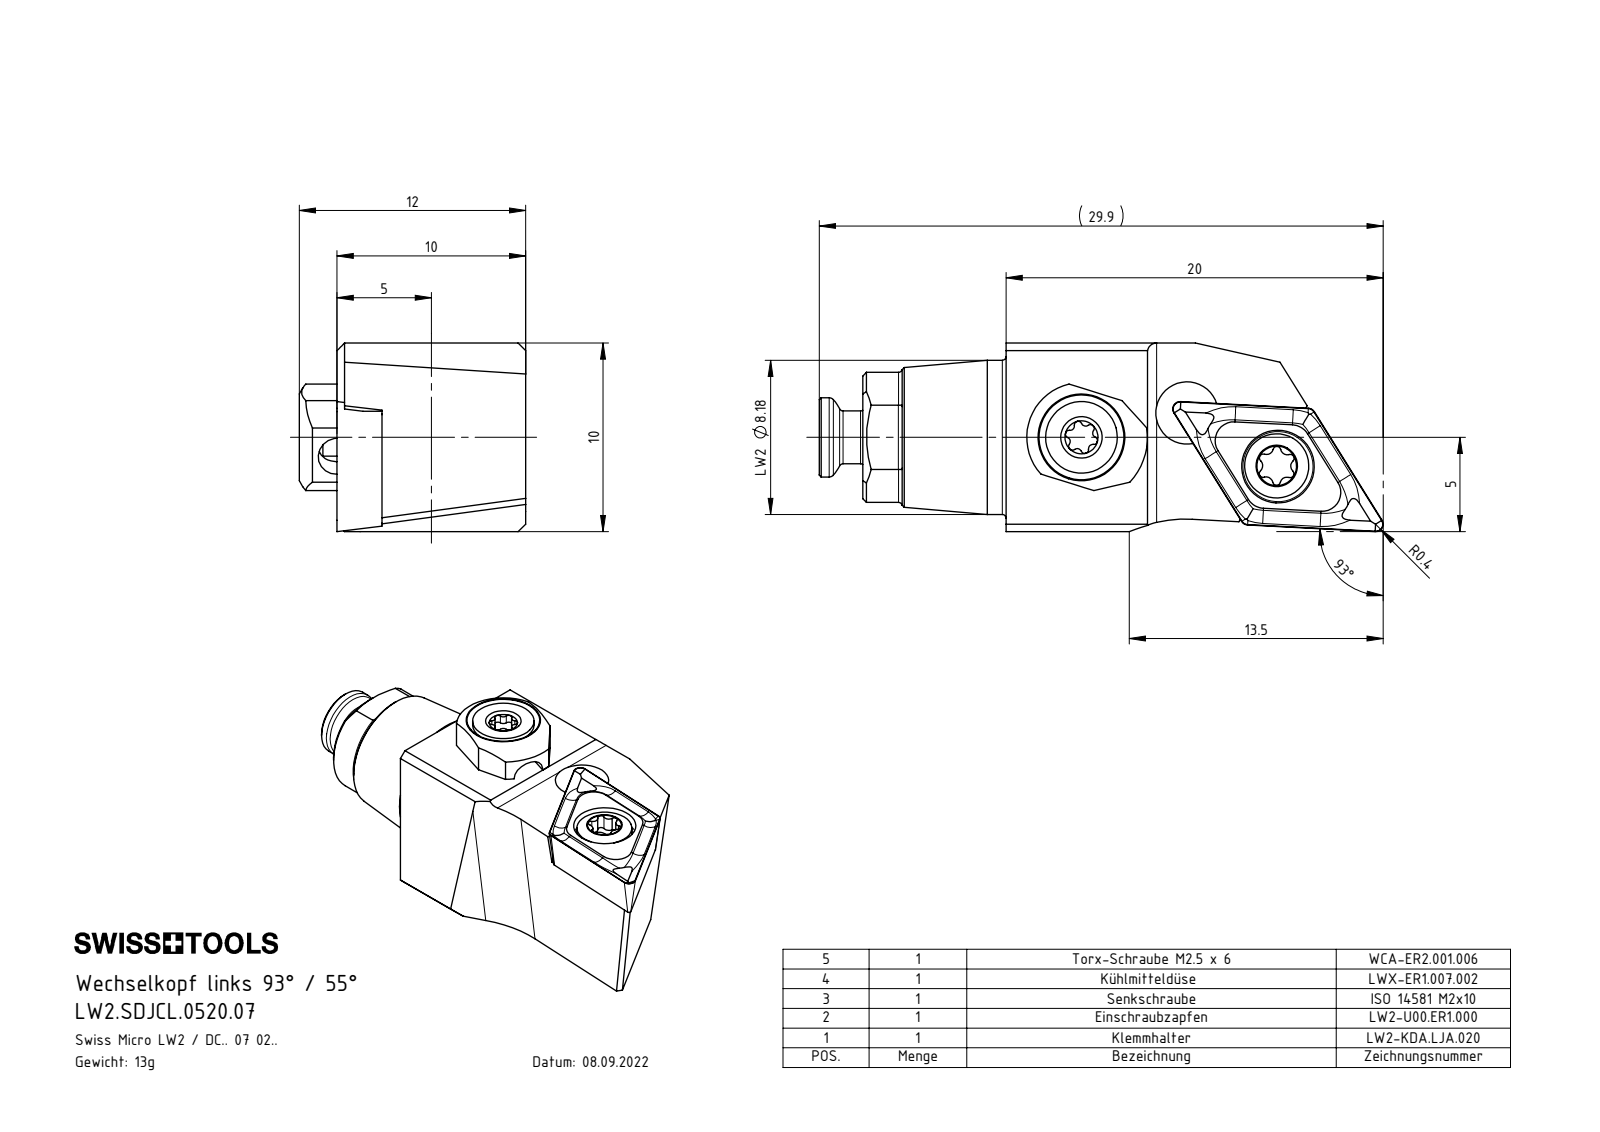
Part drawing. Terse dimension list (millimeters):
name: LWX-ER1.007.002; LW2-U00.ER1.000_A; ISO 14581 - M2x10; WCA-ER2.001.006_B (+3 more)
written by: SolidWorks 2022 (CONFIG_CONTROL_DESIGN)
unit: mm
bodies: 6 solids, 259 faces (66 planar, 93 cylindrical, 100 other)
size: 29.9 × 12 × 10
volume: 1 785 mm³; area: 1 723 mm²
holes: 1× ⌀1, 1× ⌀1.5, 1× ⌀1.6, 1× ⌀2.05, 1× ⌀2.8, 1× ⌀3, 1× ⌀3.3, 1× ⌀3.5, 1× ⌀3.85
bosses: 1× ⌀8.18, 1× ⌀4.2, 1× ⌀4, 1× ⌀3.8, 1× ⌀3.4, 1× ⌀3, 1× ⌀2.8, 1× ⌀2.5
rounds: 8× R0.2, 6× R0.19, 6× R0.21, 6× R0.24, 6× R0.29, 5× R0.36, 1× R0.36, 1× R0.5
face distances: 10, 7.62, 2.38, 9.6, 1.98, 0.4, 7.6, 2, 1.1, 8
hole spacings: 5.52, 5.59, 5.75, 10.47, 10.53
